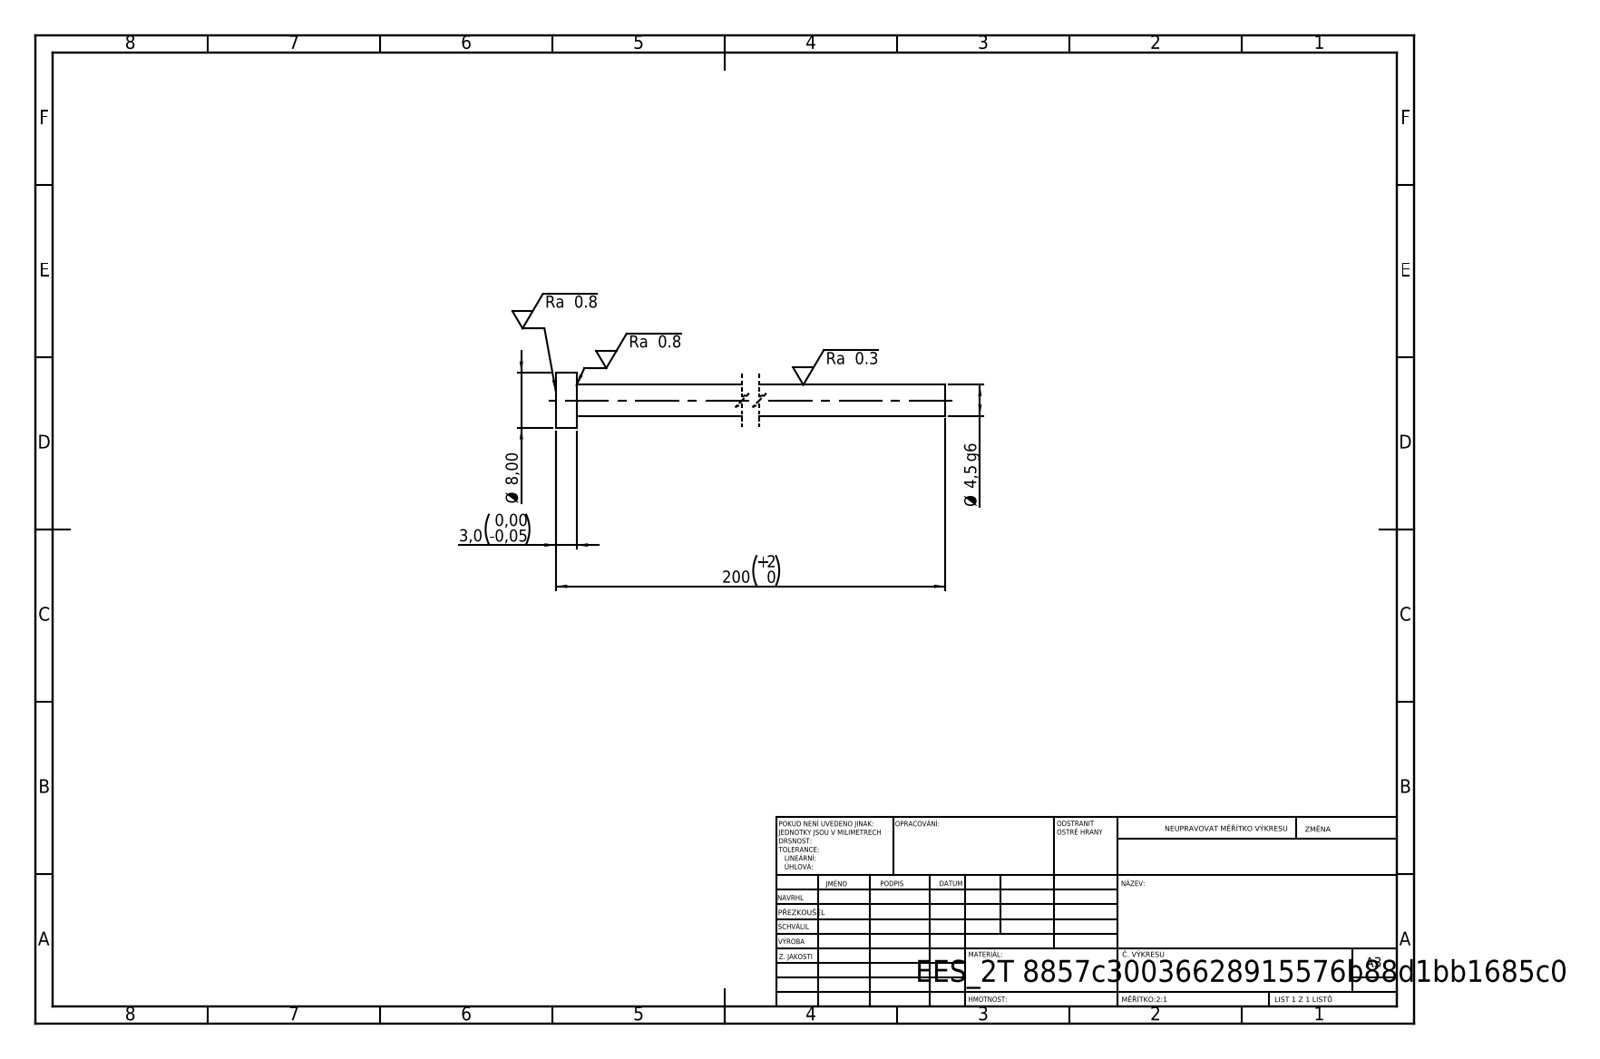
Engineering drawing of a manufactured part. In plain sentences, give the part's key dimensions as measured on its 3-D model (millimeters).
Its 3-D file was written by "SolidWorks 2019 (CONFIG_CONTROL_DESIGN)". It is 1 solid with 7 faces: 3 planar, 4 cylindrical and 0 other. Overall it measures 200 by 8 by 8 millimeters. Its volume is 3 284 cubic millimeters and its surface area 2 961 square millimeters. Round bosses or shafts: 1 of diameter 8, 1 of diameter 4.5. The main face-to-face distances are 3, 200, 197.
